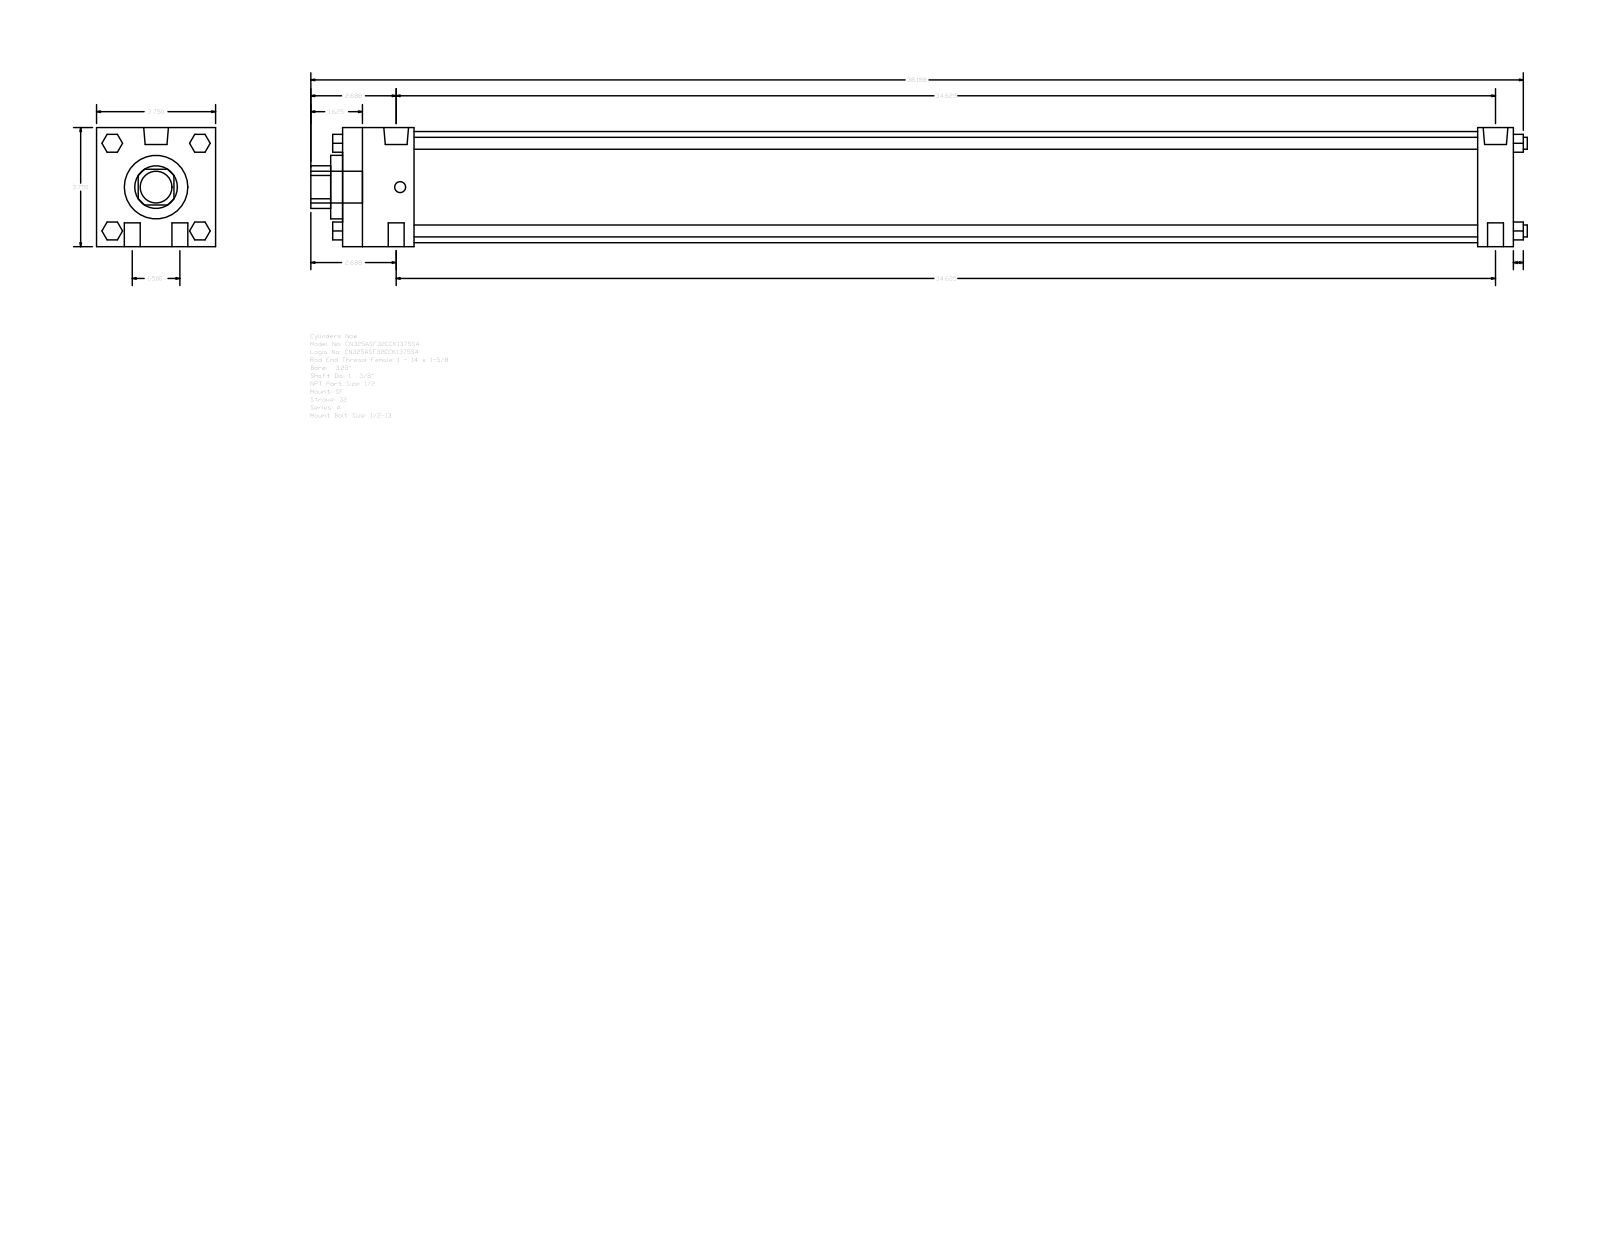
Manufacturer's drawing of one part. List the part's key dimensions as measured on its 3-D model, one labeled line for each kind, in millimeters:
Part name (STEP PRODUCT): A_SF__0325_1.375
STEP written by: GSSL Pune (CONFIG_CONTROL_DESIGN)
Units: millimetres
Bodies: 0 solids, 124 faces (94 planar, 30 cylindrical, 0 other)
Overall size (bounding box): 973.14 × 95.25 × 95.25
Round holes (diameter × count): ⌀34.92 ×1, ⌀50.8 ×1, ⌀88.9 ×1
Round bosses / shafts (diameter × count): ⌀12.7 ×4, ⌀9.53 ×4, ⌀19.77 ×2, ⌀8.73 ×2, ⌀25.4 ×1
Partial cylindrical surfaces — rounded edges, fillets, slot ends (radius × count): R17.06 ×1
Main face-to-face distances: 95.24, 936.62, 28.57, 908.05, 57.15, 850.9, 879.47, 9.52, 66.67, 917.57
